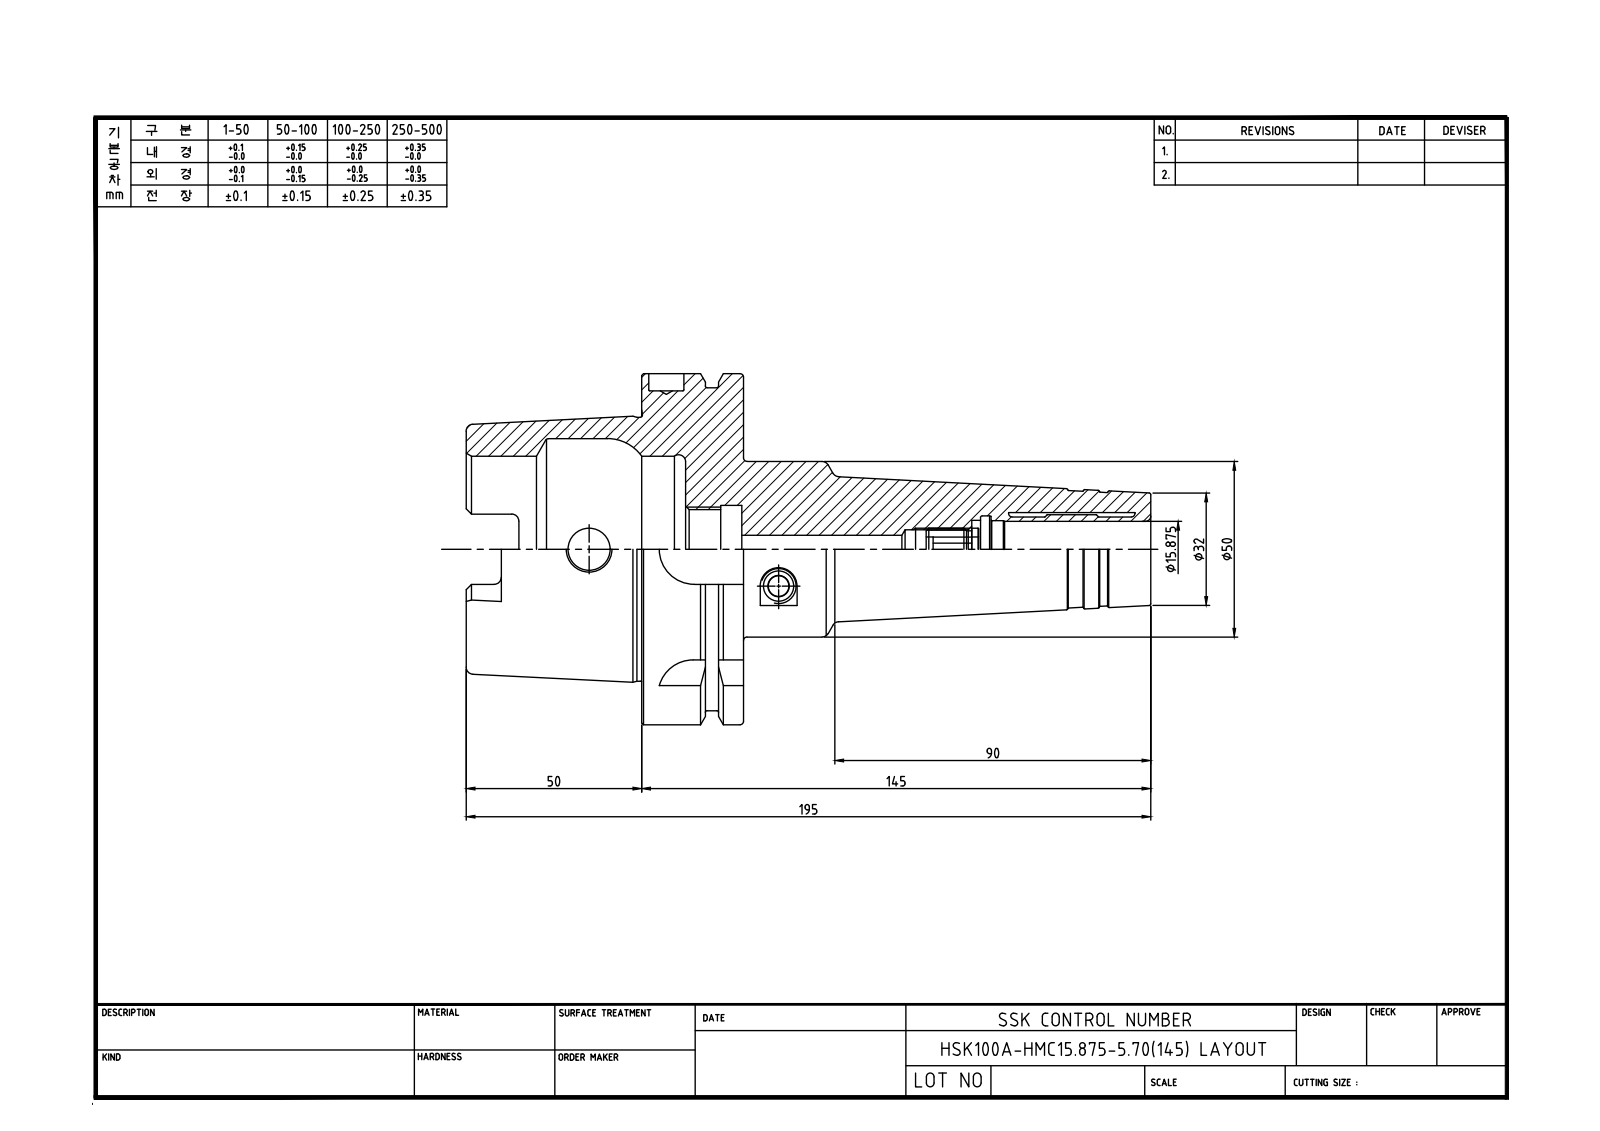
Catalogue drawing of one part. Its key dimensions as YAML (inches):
part_name: "LO-HSK100A-HMC15.875-145"
step_written_by: "Autodesk Inventor 2025 (AUTOMOTIVE_DESIGN)"
units: inches
bodies: {solids: 1, faces: 135, planar: 38, cylindrical: 35, other: 62}
overall_size: [7.677, 3.937, 3.937]
volume: 23.55
surface_area: 104.7
round_holes:
  - {diameter: 0.315, count: 1}
  - {diameter: 0.394, count: 1}
  - {diameter: 0.43, count: 1}
  - {diameter: 0.472, count: 1}
  - {diameter: 0.625, count: 1}
  - {diameter: 0.646, count: 1}
  - {diameter: 0.881, count: 1}
  - {diameter: 0.984, count: 1}
  - {diameter: 2.087, count: 1}
  - {diameter: 2.48, count: 1}
round_bosses_or_shafts:
  - {diameter: 3.937, count: 1}
  - {diameter: 3.622, count: 1}
  - {diameter: 2.969, count: 1}
  - {diameter: 1.969, count: 1}
partial_cylinders:
  - {radius: 0.079, count: 6}
  - {radius: 0.192, count: 4}
  - {radius: 0.394, count: 4}
face_to_face_distances: [1.142, 0.492, 0.65, 2.461, 1.969, 3.11, 7.677, 5.709, 5.217, 4.567]
